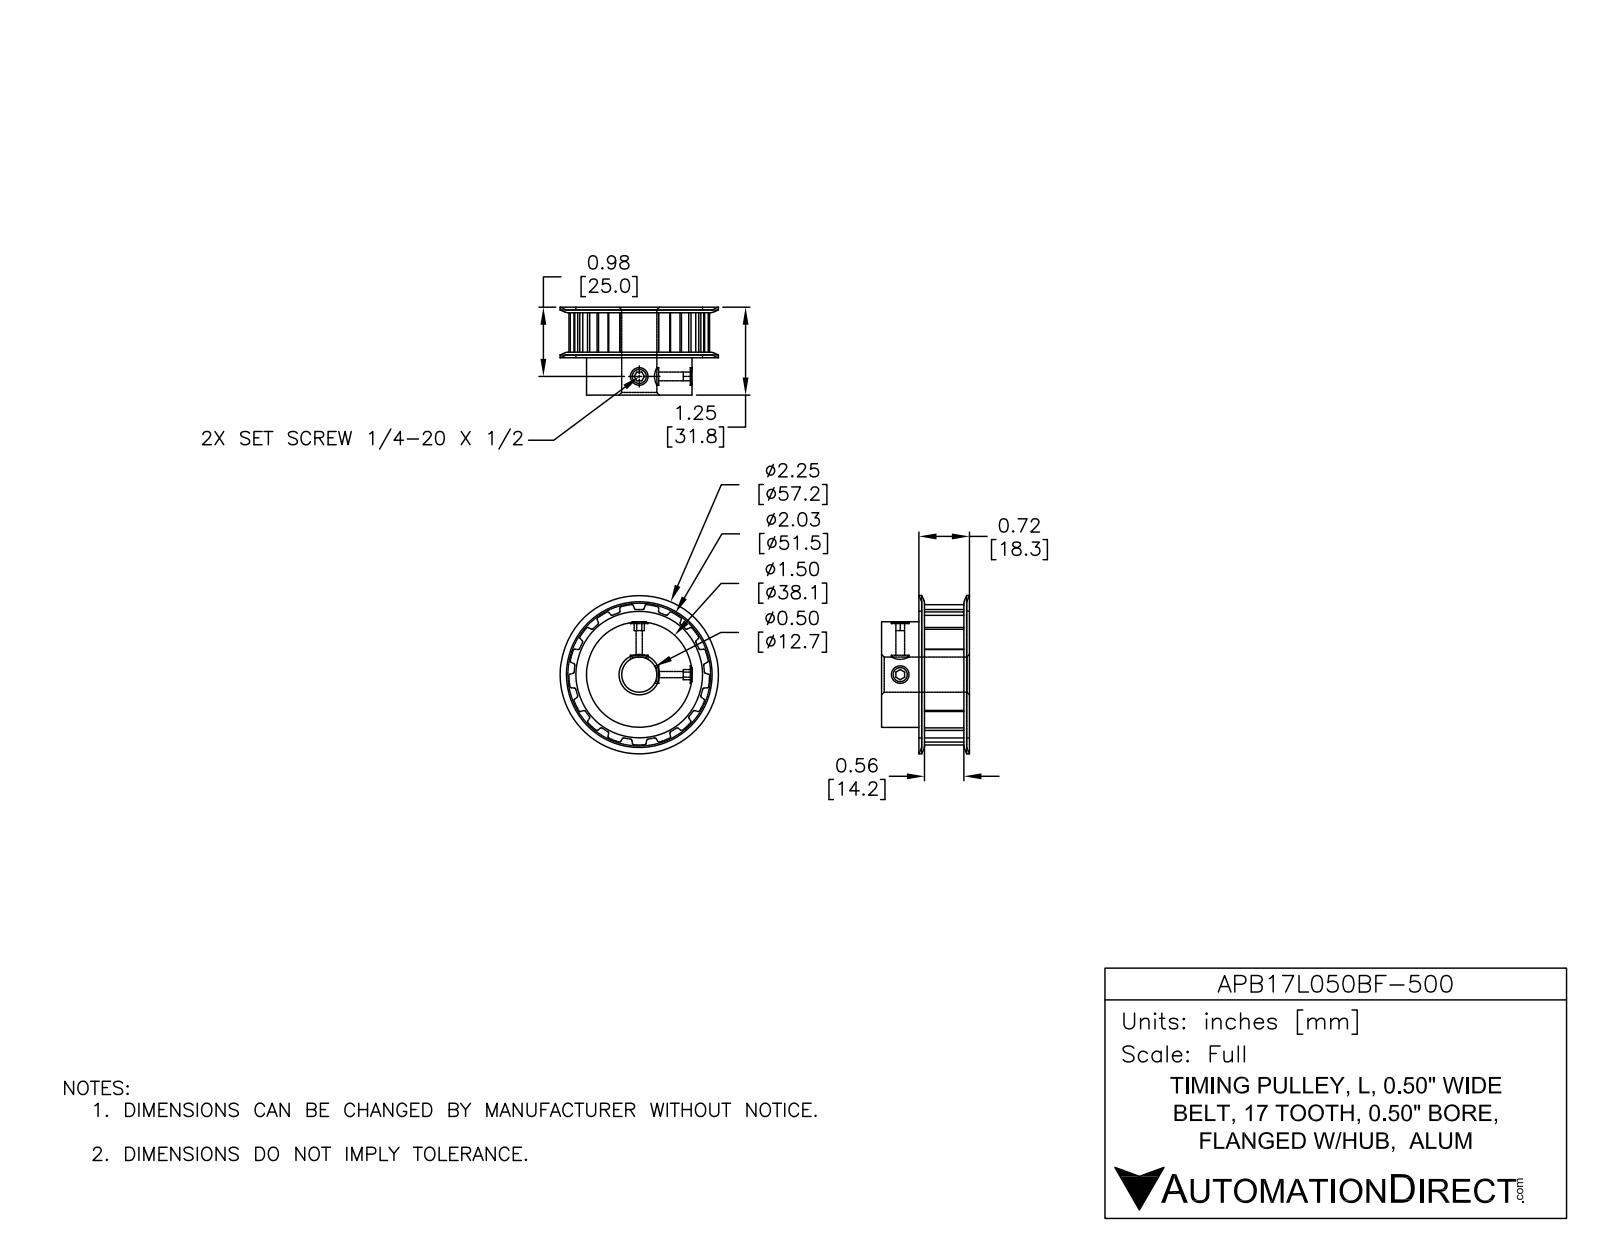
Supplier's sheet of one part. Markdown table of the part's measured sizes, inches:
| quantity | value |
| --- | --- |
| part name | APB17L050BF-500 |
| STEP written by | SolidWorks 2014 (AUTOMOTIVE_DESIGN) |
| units | inches |
| bodies | 1 solid, 148 faces (57 planar, 69 cylindrical, 22 other) |
| overall size | 2.25 × 2.25 × 1.25 |
| volume | 2.869 in³ |
| surface area | 19.08 in² |
| round holes (diameter × count) | 0.088 × 2, 0.5 × 1 |
| round bosses / shafts (diameter × count) | 1.5 × 1 |
| partial cylindrical surfaces (radius × count) | 0.015 × 34, 0.944 × 1 |
| main face-to-face distances | 0.68, 0.04, 0.64, 1.25, 1.21, 0.57, 0.04, 0.6, 0.64, 0.61 |
